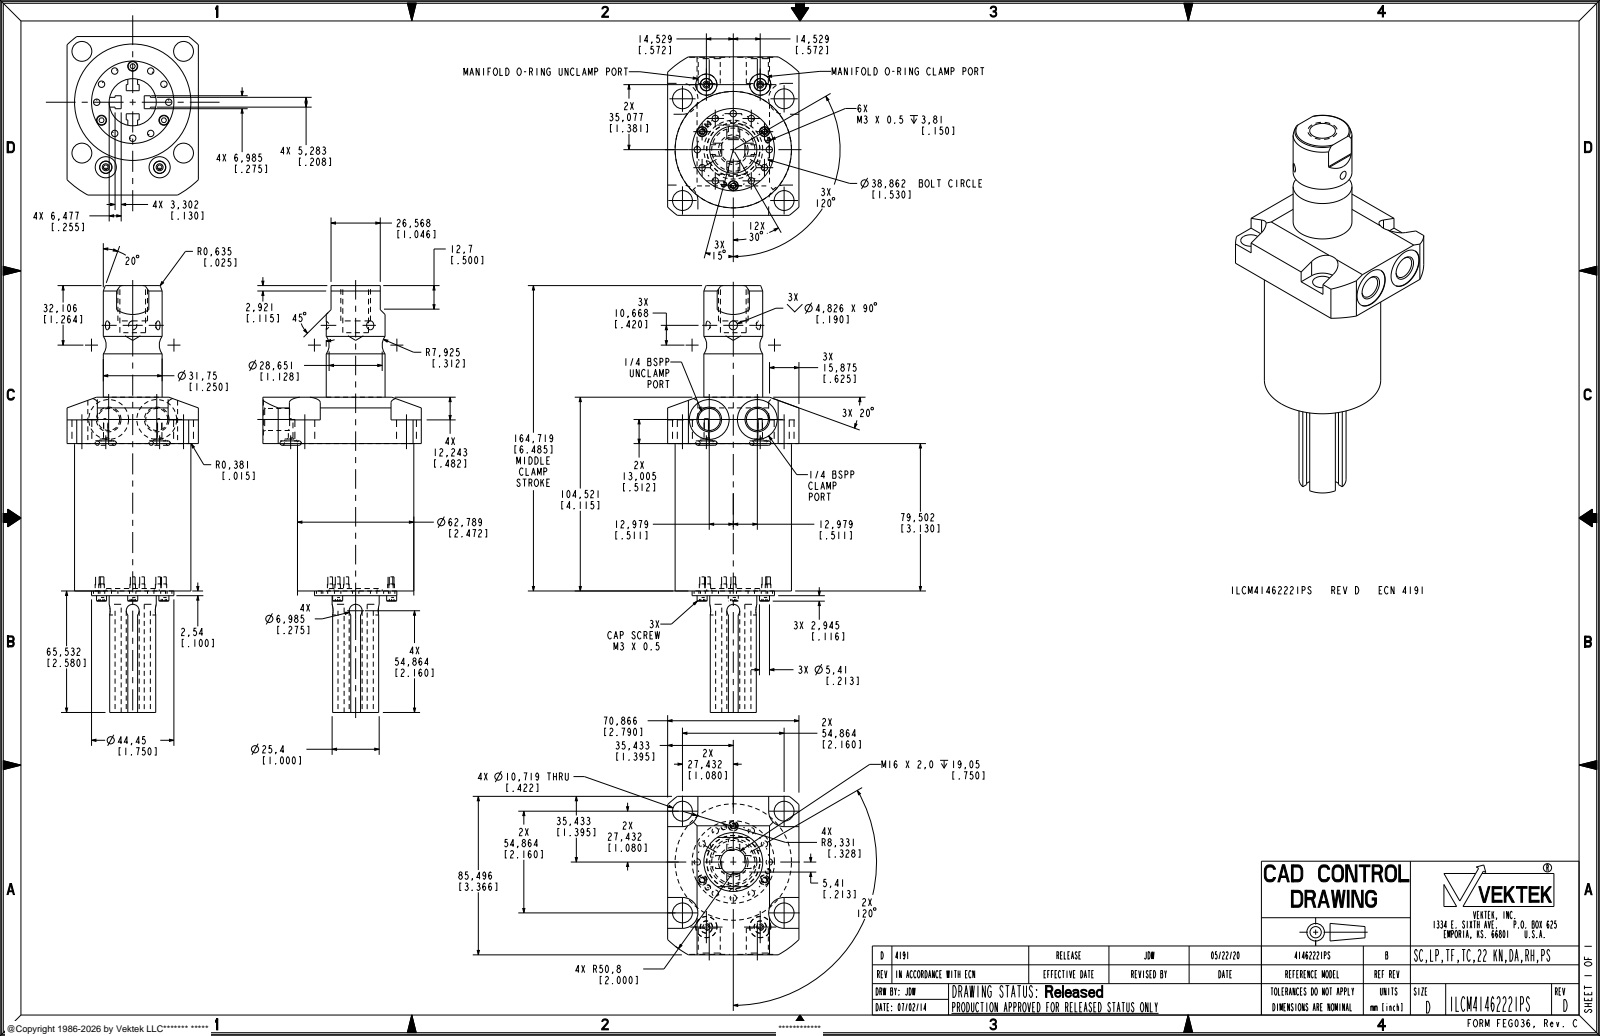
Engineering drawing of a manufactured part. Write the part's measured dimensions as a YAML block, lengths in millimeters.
part_name: "ILCM41462221PS"
step_written_by: "PRO/ENGINEER BY PARAMETRIC TECHNOLOGY CORPORATION, 2013320 (AUTOMOTIVE_DESIGN)"
units: millimeters
bodies: {solids: 3, faces: 278, planar: 126, cylindrical: 114, other: 38}
overall_size: [230.25, 85.5, 70.87]
volume: 436590
surface_area: 56055
round_holes:
  - {diameter: 3.45, count: 12}
  - {diameter: 2.54, count: 6}
  - {diameter: 10.72, count: 4}
  - {diameter: 2.49, count: 2}
  - {diameter: 6.5, count: 2}
  - {diameter: 11.4, count: 2}
  - {diameter: 11.89, count: 2}
  - {diameter: 21.49, count: 2}
  - {diameter: 13.87, count: 1}
  - {diameter: 28.7, count: 1}
round_bosses_or_shafts:
  - {diameter: 3, count: 6}
  - {diameter: 5.41, count: 3}
  - {diameter: 62.79, count: 1}
  - {diameter: 44.45, count: 1}
  - {diameter: 31.75, count: 1}
  - {diameter: 25.4, count: 1}
  - {diameter: 23.29, count: 1}
  - {diameter: 16, count: 1}
partial_cylinders:
  - {radius: 8.33, count: 4}
  - {radius: 0.7, count: 2}
  - {radius: 3.49, count: 2}
  - {radius: 50.8, count: 1}
face_to_face_distances: [25.02, 79.5, 104.52, 2.73, 9.71, 3.58, 8.86, 0.85, 6.13, 70.86]
hole_center_spacings: [19.43, 33.66, 10.06, 19.44, 20.64, 27.49, 28.57, 37.54]
